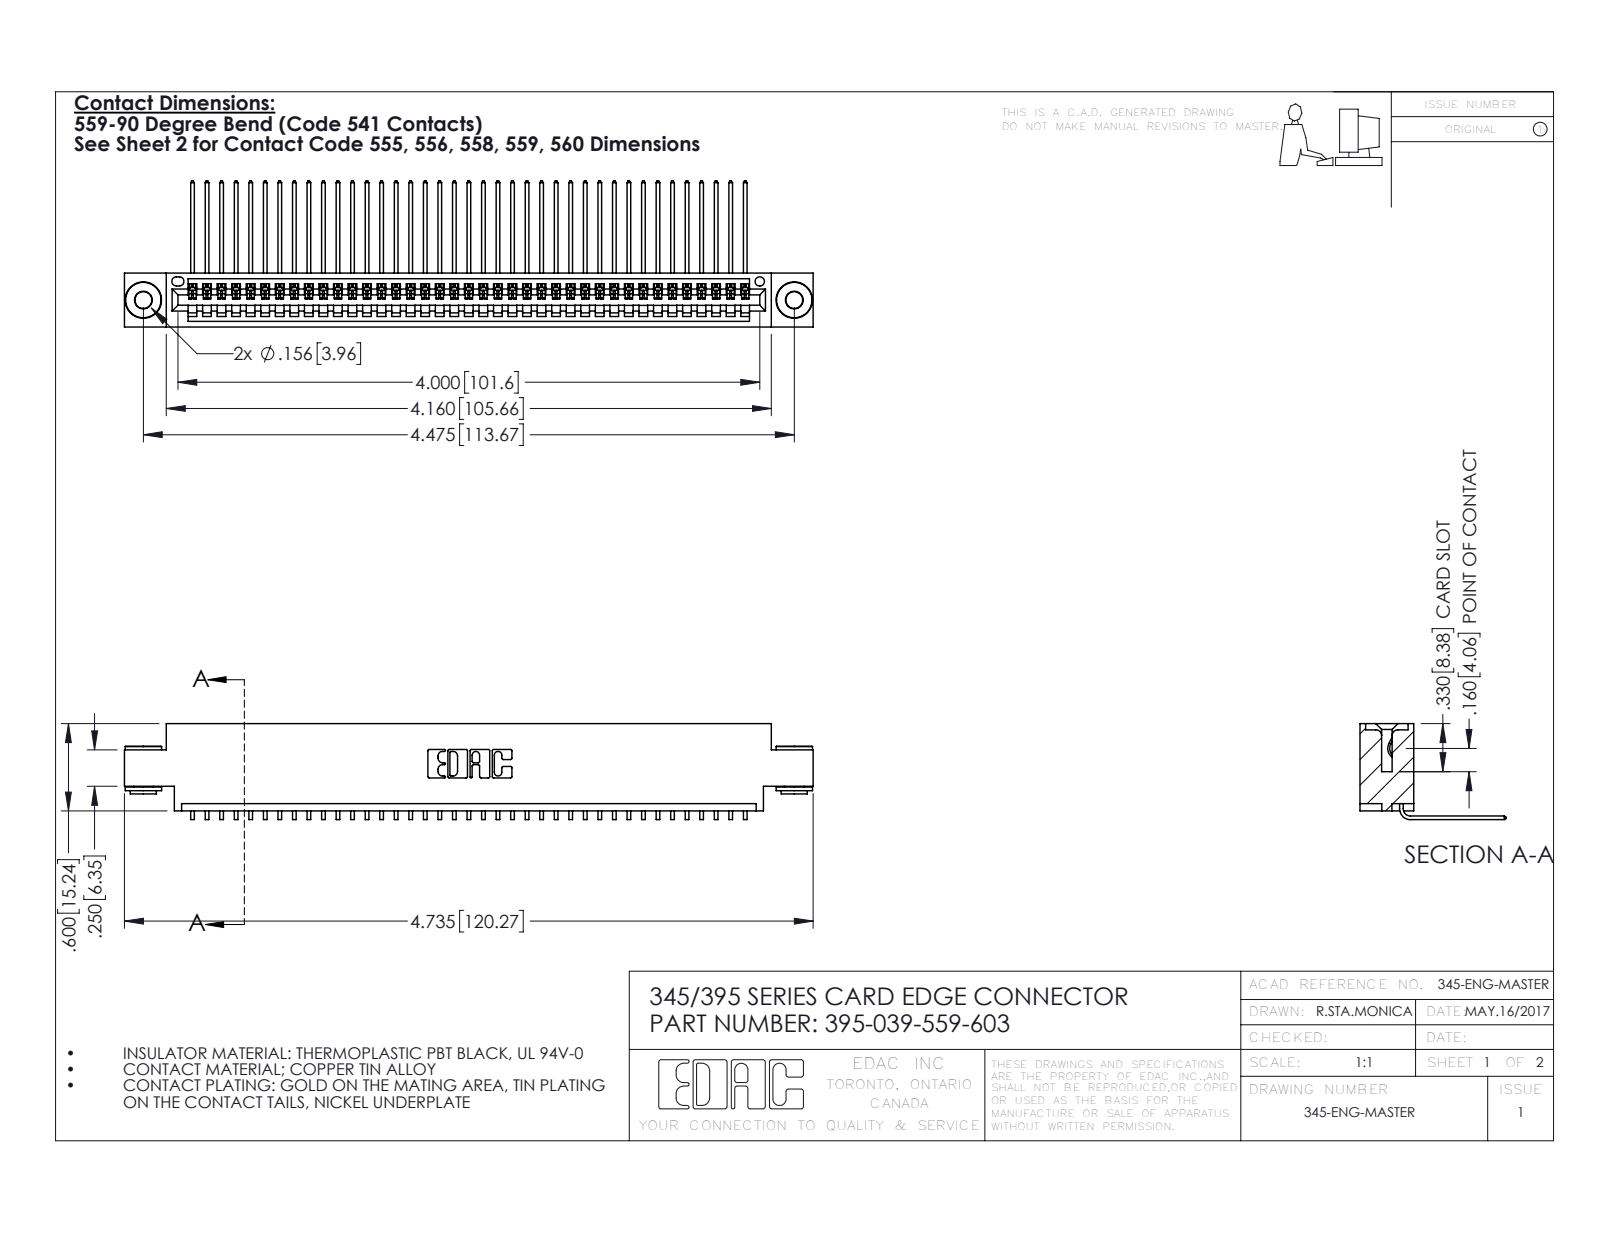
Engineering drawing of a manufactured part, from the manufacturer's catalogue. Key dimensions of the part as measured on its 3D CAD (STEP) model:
Part name (STEP PRODUCT): 395-039-559-603; 345-250-002_345-250-002-102; 345-292-001_558 559 Tail - 1; 345 Part_0.170 Offset - 0.156 Dia-TH
STEP written by: SolidWorks 2016 (CONFIG_CONTROL_DESIGN)
Units: inches
Bodies: 42 solids, 2508 faces (1732 planar, 768 cylindrical, 8 other)
Overall size (bounding box): 4.735 × 1.005 × 0.659
Volume: 0.698 in³ · Surface area: 25.2 in²
Round holes (diameter × count): ⌀0.116 ×2, ⌀0.156 ×2, ⌀0.064 ×1
Round bosses / shafts (diameter × count): ⌀0.25 ×2, ⌀0.18 ×2, ⌀0.136 ×2
Partial cylindrical surfaces — rounded edges, fillets, slot ends (radius × count): R0.006 ×78, R0.01 ×22, R0.007 ×6, R0.031 ×6, R0.026 ×3, R0.031 ×2, R0.04 ×2, R0.014 ×1
Main face-to-face distances: 0.072, 0.298, 0.37, 0.2, 0.098, 0.272, 0.025, 0.225, 0.175, 0.149
Hole centre spacings: 0.27, 4.239, 4.475
